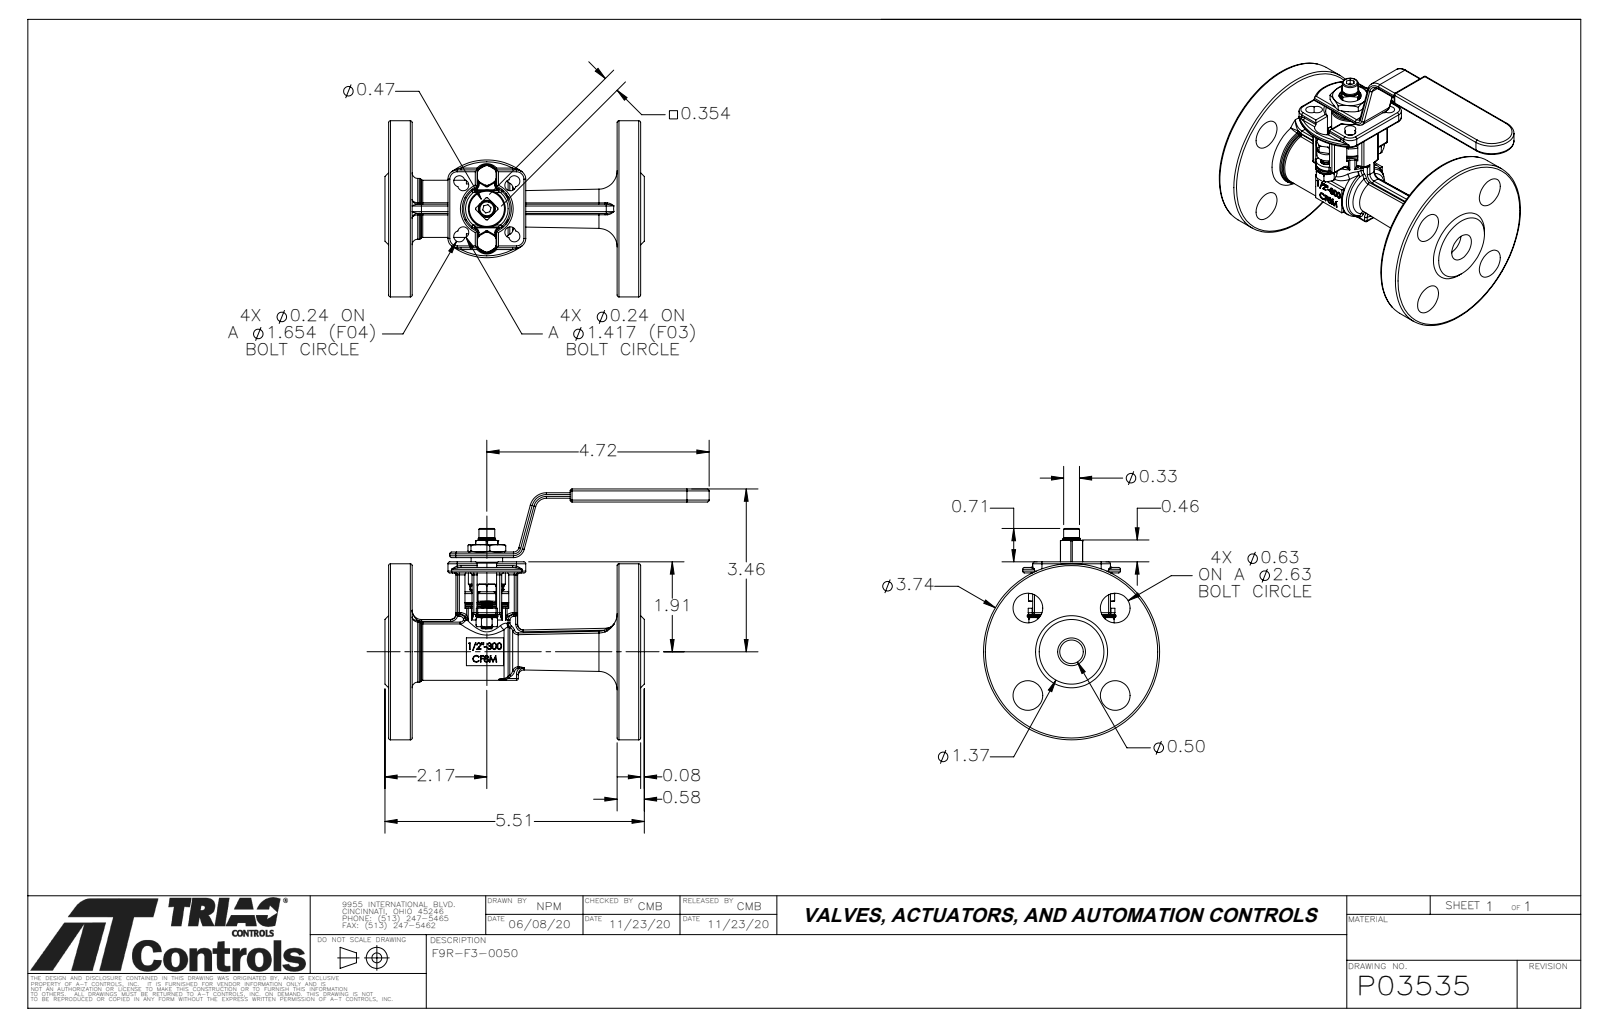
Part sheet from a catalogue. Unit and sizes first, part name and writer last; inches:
Units: inches
Overall size (bounding box): 6.89 × 5.327 × 3.74
Round holes (diameter × count): ⌀0.63 ×4, ⌀0.24 ×2, ⌀0.244 ×2, ⌀0.26 ×2, ⌀0.165 ×1, ⌀0.201 ×1, ⌀0.217 ×1, ⌀0.413 ×1, ⌀0.476 ×1, ⌀0.477 ×1, ⌀0.5 ×1, ⌀0.512 ×1
Round bosses / shafts (diameter × count): ⌀0.906 ×2, ⌀0.465 ×2, ⌀0.236 ×2, ⌀3.74 ×1, ⌀1.291 ×1, ⌀1.213 ×1, ⌀0.787 ×1, ⌀0.669 ×1
Partial cylindrical surfaces — rounded edges, fillets, slot ends (radius × count): R0.039 ×101, R0.02 ×46, R0.118 ×9, R0.197 ×5, R0.079 ×4, R0.236 ×4, R0.276 ×4, R0.394 ×3
Main face-to-face distances: 0.5, 4.854, 5.354, 4.354, 0.079, 0.118, 0.197, 0.276, 0.039, 1.142
Hole centre spacings: 1.313, 1.857, 0.709, 2.626, 1.417
Volume: 15.17 in³ · Surface area: 152.5 in²
Bodies: 24 solids, 1300 faces (320 planar, 455 cylindrical, 525 other)
Part name (STEP PRODUCT): F9R-F3-0050 BELLEVILLE WASHERS; F9R-F3-0050 STEM EXT; F9R-F3-0050_0; F9R-F3-0050 STEM (+8 more)
STEP written by: SolidWorks 2019 (CONFIG_CONTROL_DESIGN)
